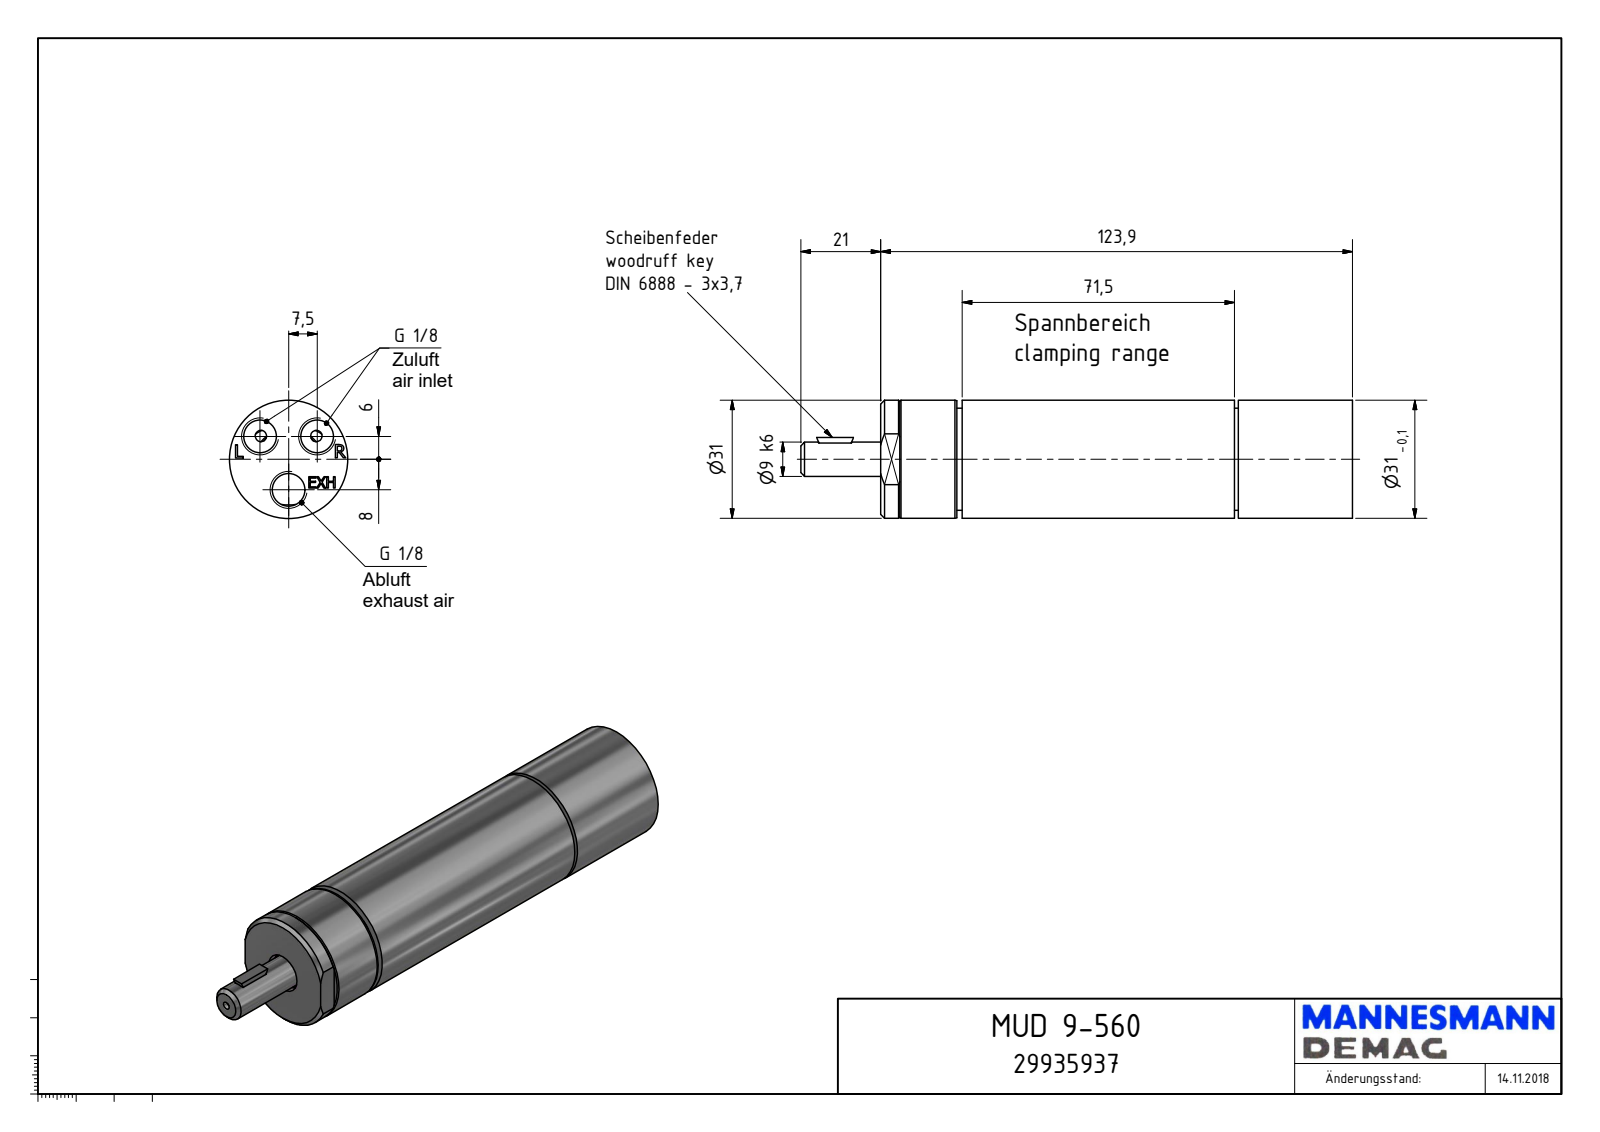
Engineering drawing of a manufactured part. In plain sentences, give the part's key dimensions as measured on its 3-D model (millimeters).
The part is named "MUD 9-560_29935937". Its 3-D file was written by "Autodesk Inventor 2018 (AUTOMOTIVE_DESIGN)". It is 1 solid with 156 faces: 93 planar, 25 cylindrical and 38 other. Overall it measures 144.9 by 31 by 31 millimeters. Its volume is 92 706 cubic millimeters and its surface area 16 664 square millimeters. Round holes: 3 of diameter 8.57, 1 of diameter 1, 1 of diameter 10.36, 1 of diameter 10.5, 1 of diameter 13.36, 1 of diameter 16, 1 of diameter 29.3. Round bosses or shafts: 1 of diameter 31, 1 of diameter 28, 1 of diameter 26.9, 1 of diameter 26.79, 1 of diameter 9. Partial cylindrical surfaces (rounded edges, fillets, slot ends): 1 of radius 5, 1 of radius 5.25. The main face-to-face distances are 123.9, 92.9, 31, 21.4, 71.5, 102.5, 116.78, 95.38, 23.88, 7.12. The hole center spacings are 9.6, 15.88, 8, 15.
